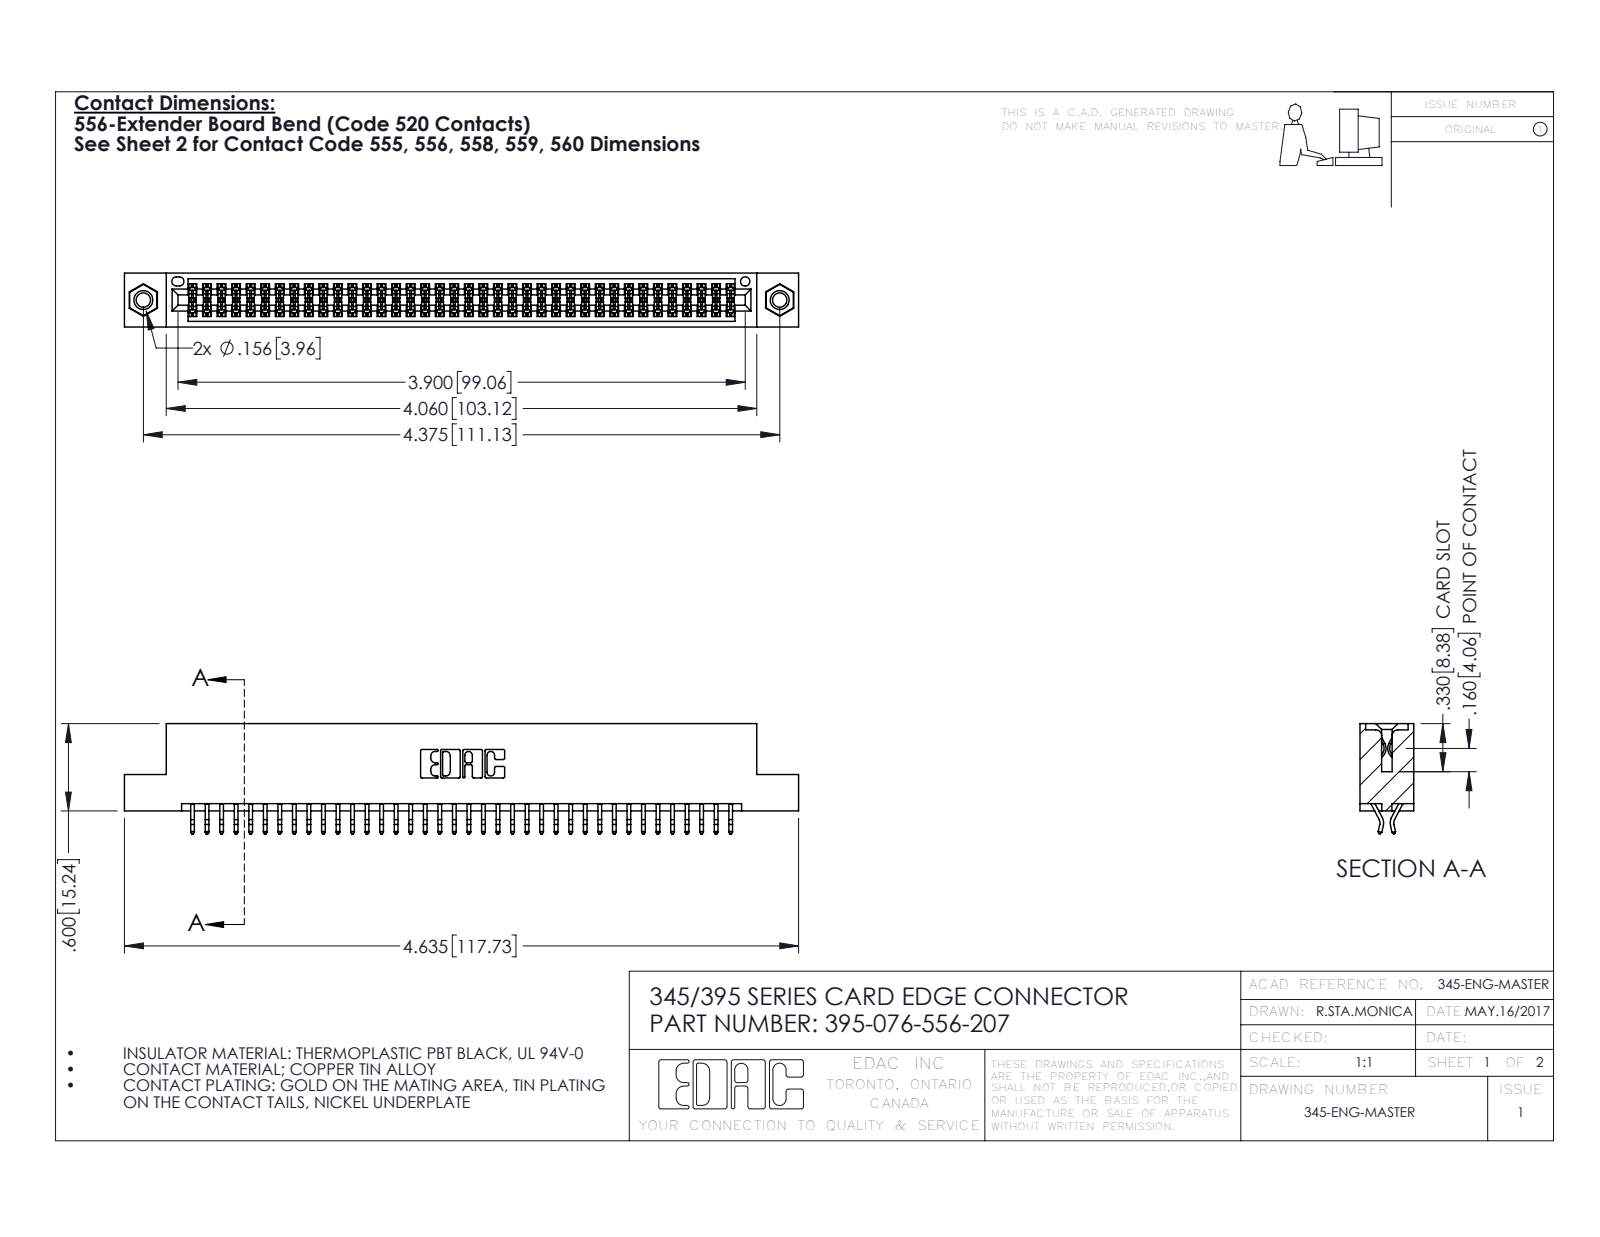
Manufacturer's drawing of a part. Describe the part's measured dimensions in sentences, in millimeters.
The part is named "345 Part_Flush Mounting Lugs - 0.156 Dia-TI; 395-076-556-207; 345-250-001_345-250-005-103; 345-292-001_556 Tail". Its 3-D file was written by "SolidWorks 2016 (CONFIG_CONTROL_DESIGN)". It is 79 solids with 4442 faces: 2924 planar, 1502 cylindrical and 16 other. Overall it measures 117.7 by 19.2 by 9.4 millimeters. Its volume is 11 400 cubic millimeters and its surface area 16 710 square millimeters. Round holes: 2 of diameter 2.5, 2 of diameter 3.2, 2 of diameter 4, 1 of diameter 1.6. Round bosses or shafts: 2 of diameter 3.9. Partial cylindrical surfaces (rounded edges, fillets, slot ends): 114 of radius 0.2, 22 of radius 0.3, 6 of radius 0.2, 6 of radius 0.8, 3 of radius 0.7, 2 of radius 0.3, 2 of radius 0.4, 2 of radius 0.5. The main face-to-face distances are 1.8, 7.6, 5.1, 9.4, 0.6, 2.5, 6.9, 5.7, 4.4, 3.8. The hole center spacings are 6.9, 105.1, 111.1.
